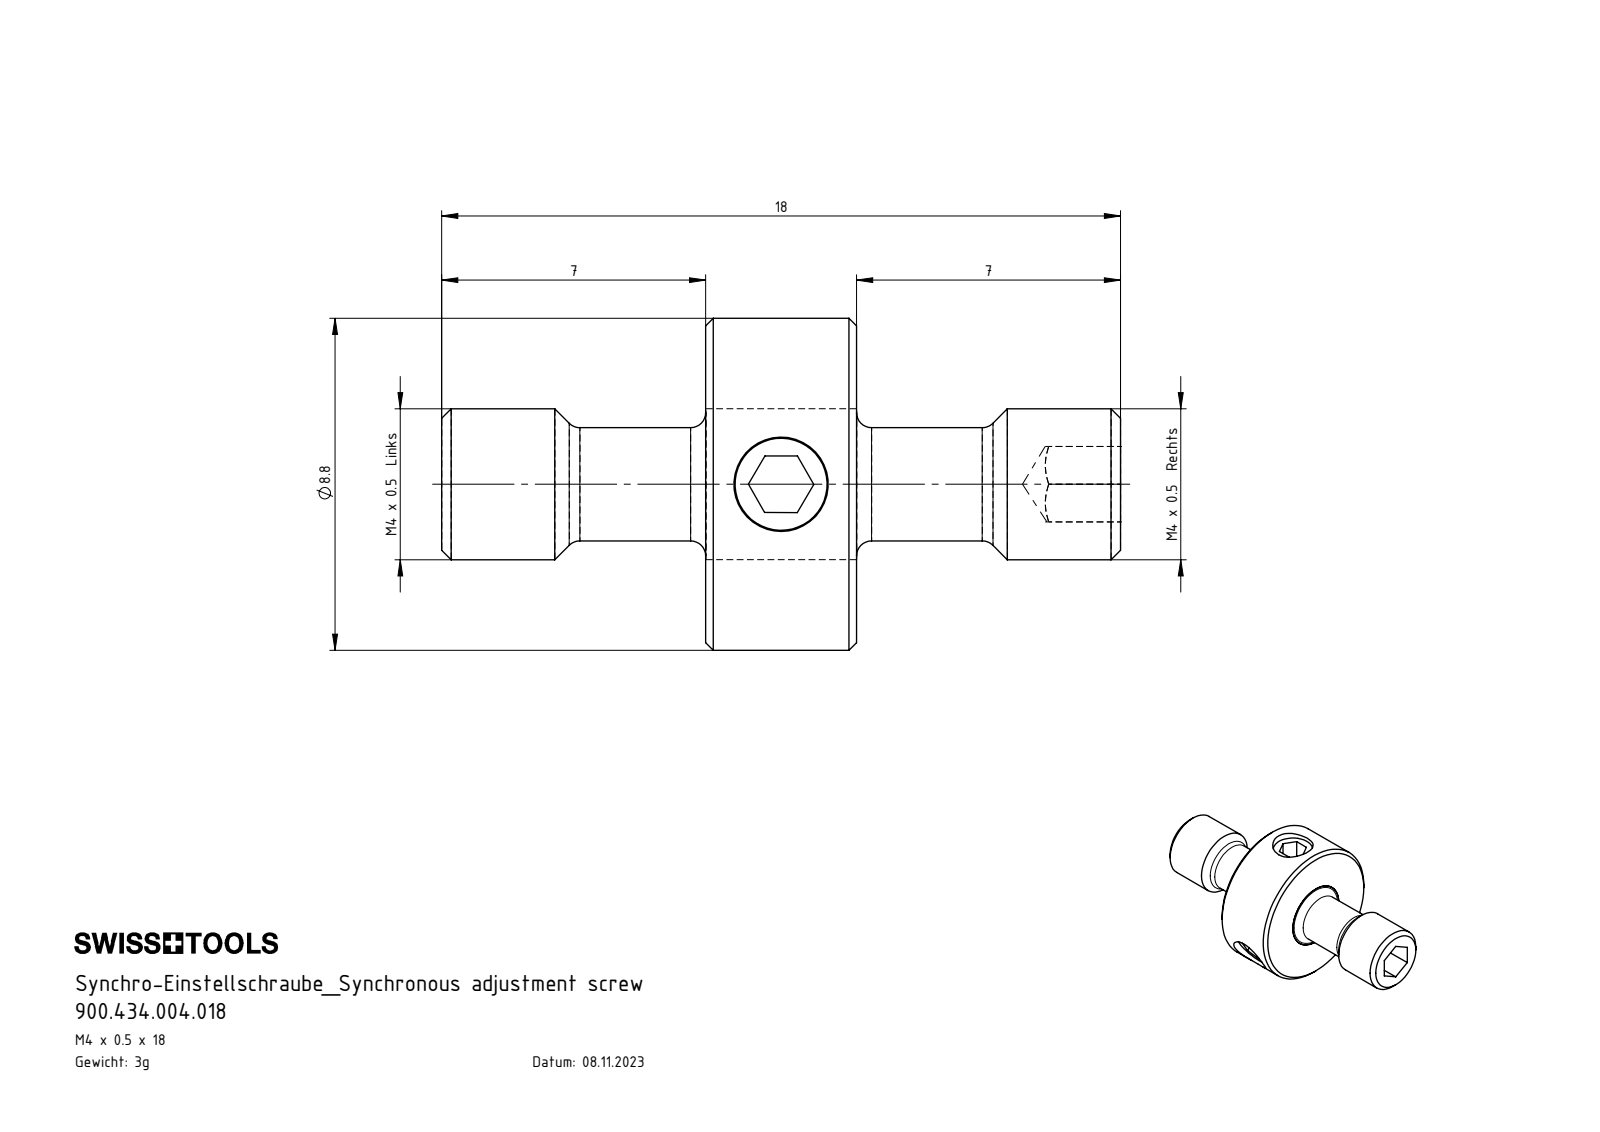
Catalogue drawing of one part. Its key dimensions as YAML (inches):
part_name: "ISO 4026 - M3 x 2; Z20-ER3.001.018_A; 900.434.004.018; Z20-ER3.002.004_A"
step_written_by: "SolidWorks 2022 (AUTOMOTIVE_DESIGN)"
units: inches
bodies: {solids: 5, faces: 96, planar: 36, cylindrical: 26, other: 34}
overall_size: [0.709, 0.346, 0.346]
volume: 0.022
surface_area: 0.986
round_holes:
  - {diameter: 0.098, count: 3}
round_bosses_or_shafts:
  - {diameter: 0.118, count: 4}
  - {diameter: 0.346, count: 1}
  - {diameter: 0.157, count: 1}
face_to_face_distances: [0.157, 0.276, 0.433, 0.059, 0.079, 0.709]
